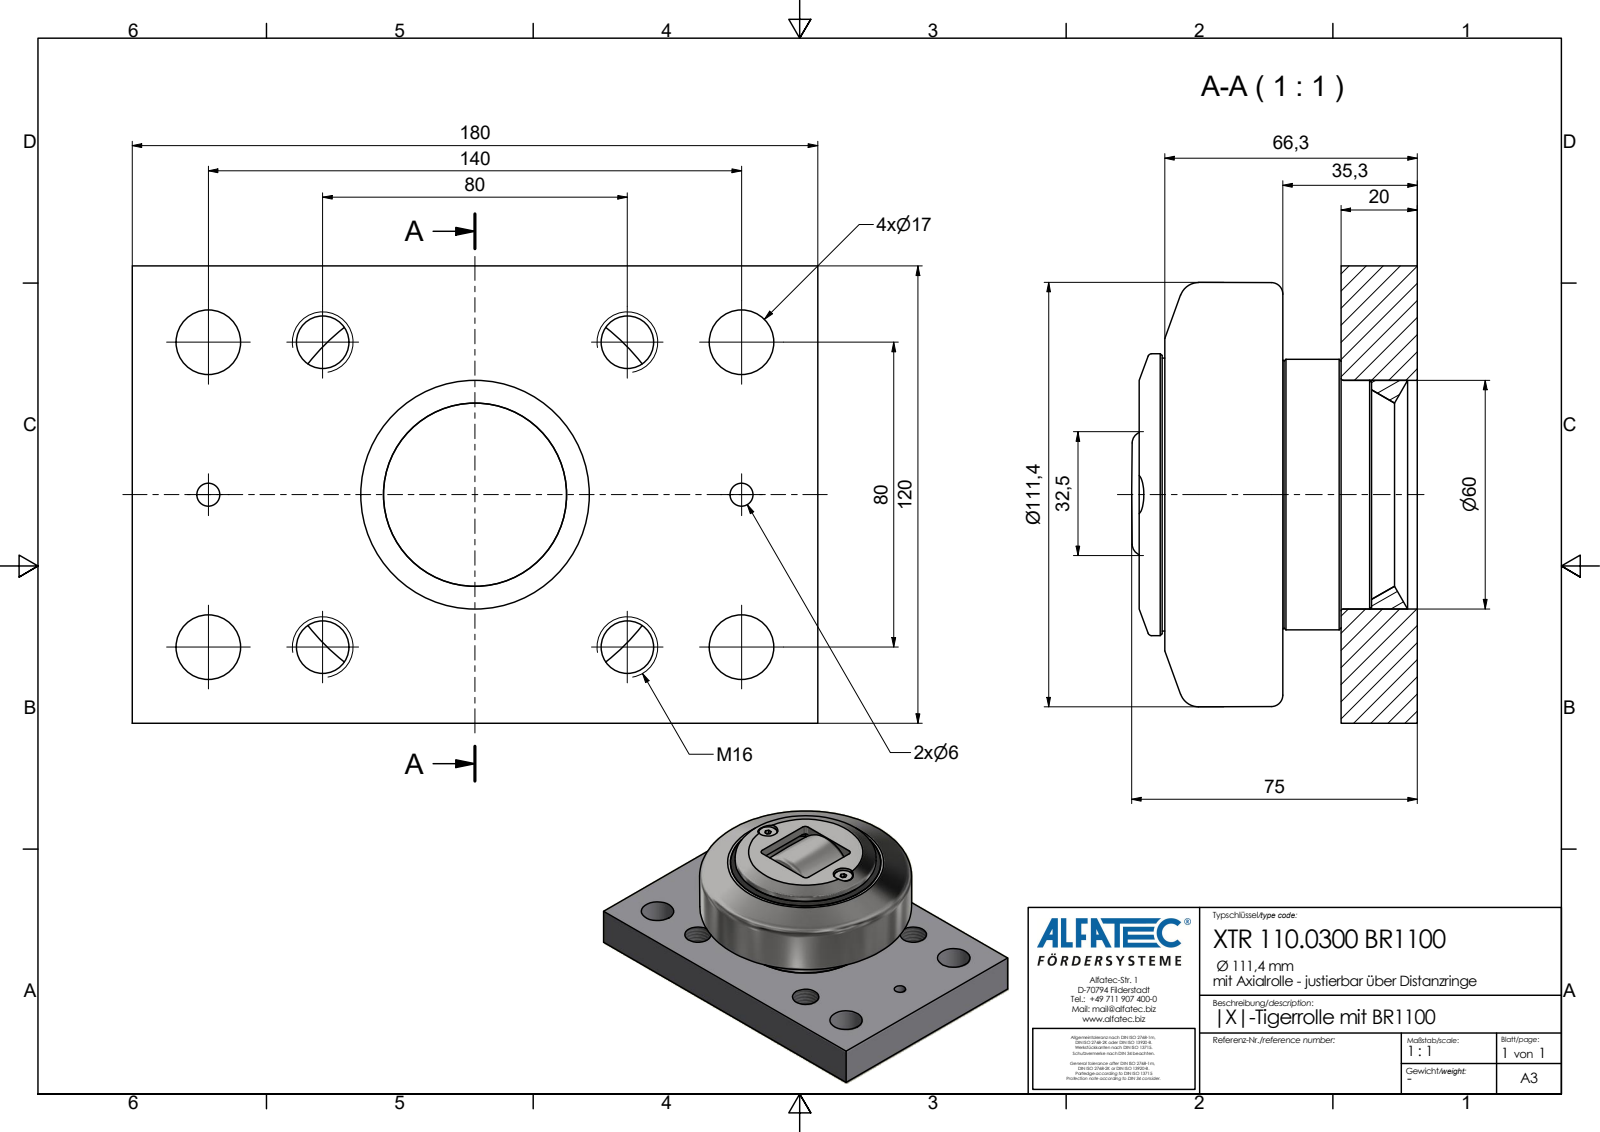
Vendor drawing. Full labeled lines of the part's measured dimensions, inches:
Part name (STEP PRODUCT): XTR 110.0300 BR1100_Kontur
STEP written by: Autodesk Inventor 2020 (AP242_MANAGED_MODEL_BASED_3D_ENGINEERING_MIM_LF)
Units: inches
Bodies: 1 solid, 88 faces (40 planar, 30 cylindrical, 18 other)
Overall size (bounding box): 7.087 × 4.724 × 2.951
Volume: 47.21 in³ · Surface area: 135.6 in²
Round holes (diameter × count): ⌀0.545 ×4, ⌀0.669 ×4, ⌀0.236 ×2, ⌀0.413 ×2
Round bosses / shafts (diameter × count): ⌀0.384 ×2, ⌀2.913 ×1, ⌀2.819 ×1, ⌀2.795 ×1, ⌀2.776 ×1
Partial cylindrical surfaces — rounded edges, fillets, slot ends (radius × count): R0.079 ×4, R0.453 ×1, R0.551 ×1, R0.945 ×1
Main face-to-face distances: 0.787, 1.39, 0.602, 4.724, 7.087, 2.872, 2.085, 1.482, 2.61, 1.823
Hole centre spacings: 3.15, 1.181, 1.575, 1.644, 1.969, 2.283, 3.106, 3.364
